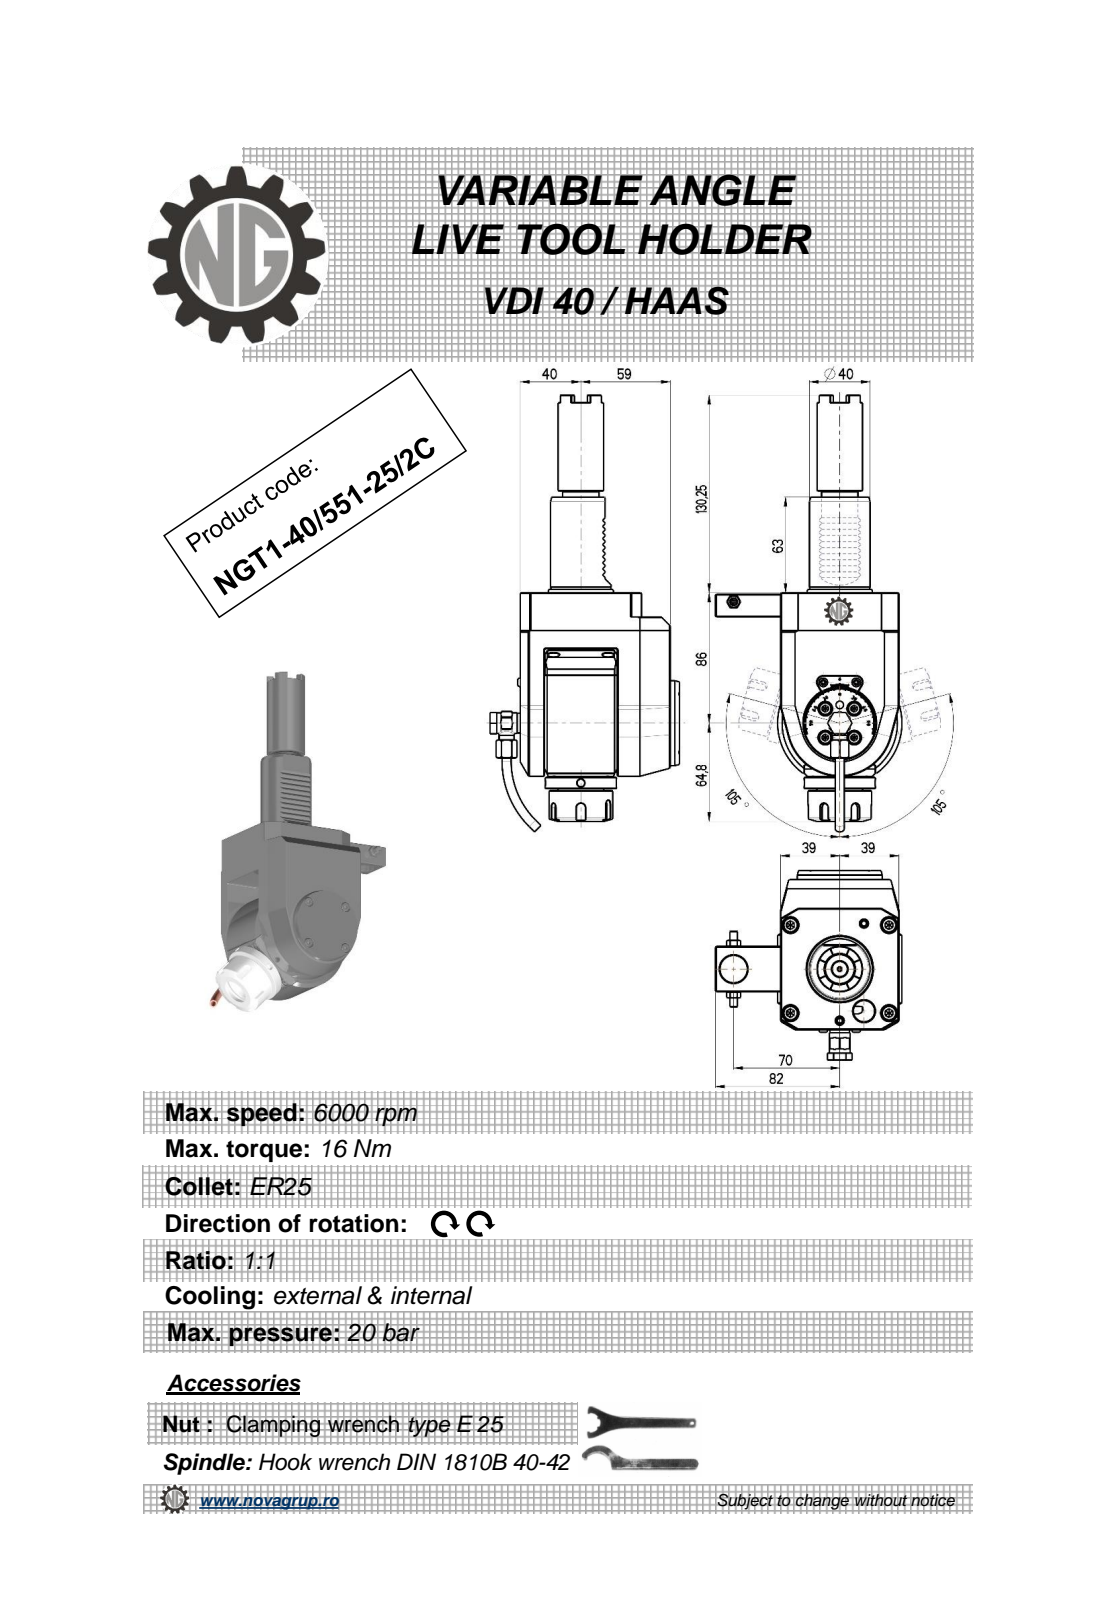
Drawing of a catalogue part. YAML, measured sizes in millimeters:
part_name: "NGT1_40_551_25_2C"
step_written_by: "PRO/ENGINEER BY PARAMETRIC TECHNOLOGY CORPORATION, 2010280 (CONFIG_CONTROL_DESIGN)"
units: millimeters
bodies: {solids: 1, faces: 617, planar: 276, cylindrical: 140, other: 201}
overall_size: [287.92, 124.9, 123]
volume: 980701
surface_area: 92567
round_holes:
  - {diameter: 4, count: 3}
  - {diameter: 5, count: 2}
  - {diameter: 3, count: 1}
  - {diameter: 4.2, count: 1}
  - {diameter: 6.2, count: 1}
  - {diameter: 9, count: 1}
  - {diameter: 9.5, count: 1}
  - {diameter: 11, count: 1}
  - {diameter: 18, count: 1}
  - {diameter: 20, count: 1}
  - {diameter: 20.3, count: 1}
round_bosses_or_shafts:
  - {diameter: 10, count: 2}
  - {diameter: 6, count: 2}
  - {diameter: 5.7, count: 2}
  - {diameter: 56, count: 1}
  - {diameter: 47, count: 1}
  - {diameter: 42, count: 1}
  - {diameter: 40, count: 1}
  - {diameter: 36, count: 1}
partial_cylinders:
  - {radius: 0.26, count: 12}
  - {radius: 0.3, count: 10}
  - {radius: 3, count: 5}
  - {radius: 0.5, count: 4}
  - {radius: 1, count: 2}
  - {radius: 10, count: 2}
  - {radius: 7.7, count: 1}
  - {radius: 35, count: 1}
face_to_face_distances: [16, 37, 64, 99, 78, 6, 105, 1, 21, 25]
hole_center_spacings: [0.4, 39.45, 49, 49.4, 70, 85.45, 85.68, 106.3]
